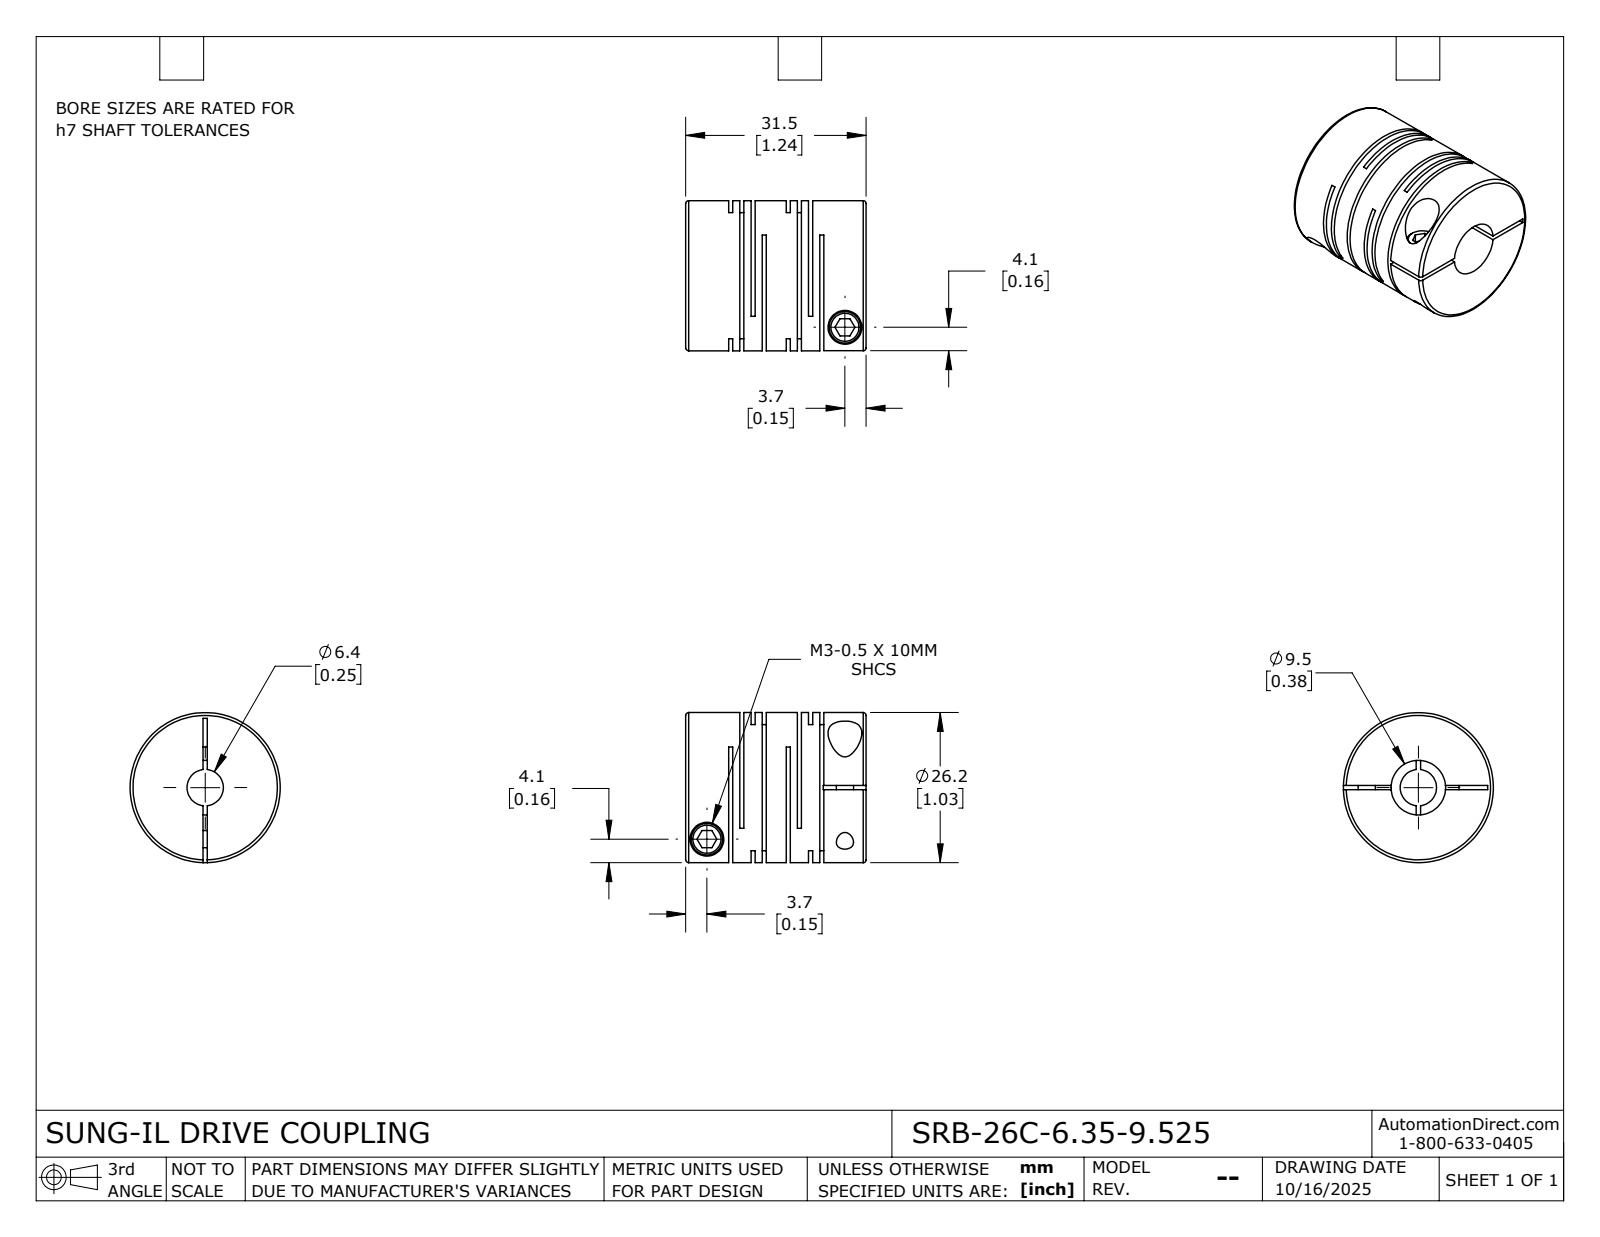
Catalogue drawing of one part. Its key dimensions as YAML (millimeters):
part_name: "SRB-26C-6.35-9.525"
step_written_by: "SolidWorks 2024 (CONFIG_CONTROL_DESIGN)"
units: millimeters
bodies: {solids: 1, faces: 115, planar: 60, cylindrical: 42, other: 13}
overall_size: [31.5, 26.2, 26.2]
volume: 12403
surface_area: 10876
round_holes:
  - {diameter: 3, count: 2}
  - {diameter: 5.9, count: 2}
  - {diameter: 6.35, count: 1}
  - {diameter: 9.53, count: 1}
round_bosses_or_shafts:
  - {diameter: 5.5, count: 2}
  - {diameter: 26.2, count: 1}
face_to_face_distances: [1.95, 10.05, 0.71, 3.9, 8.1, 12, 1.24, 2.66, 9.34, 13.95]
